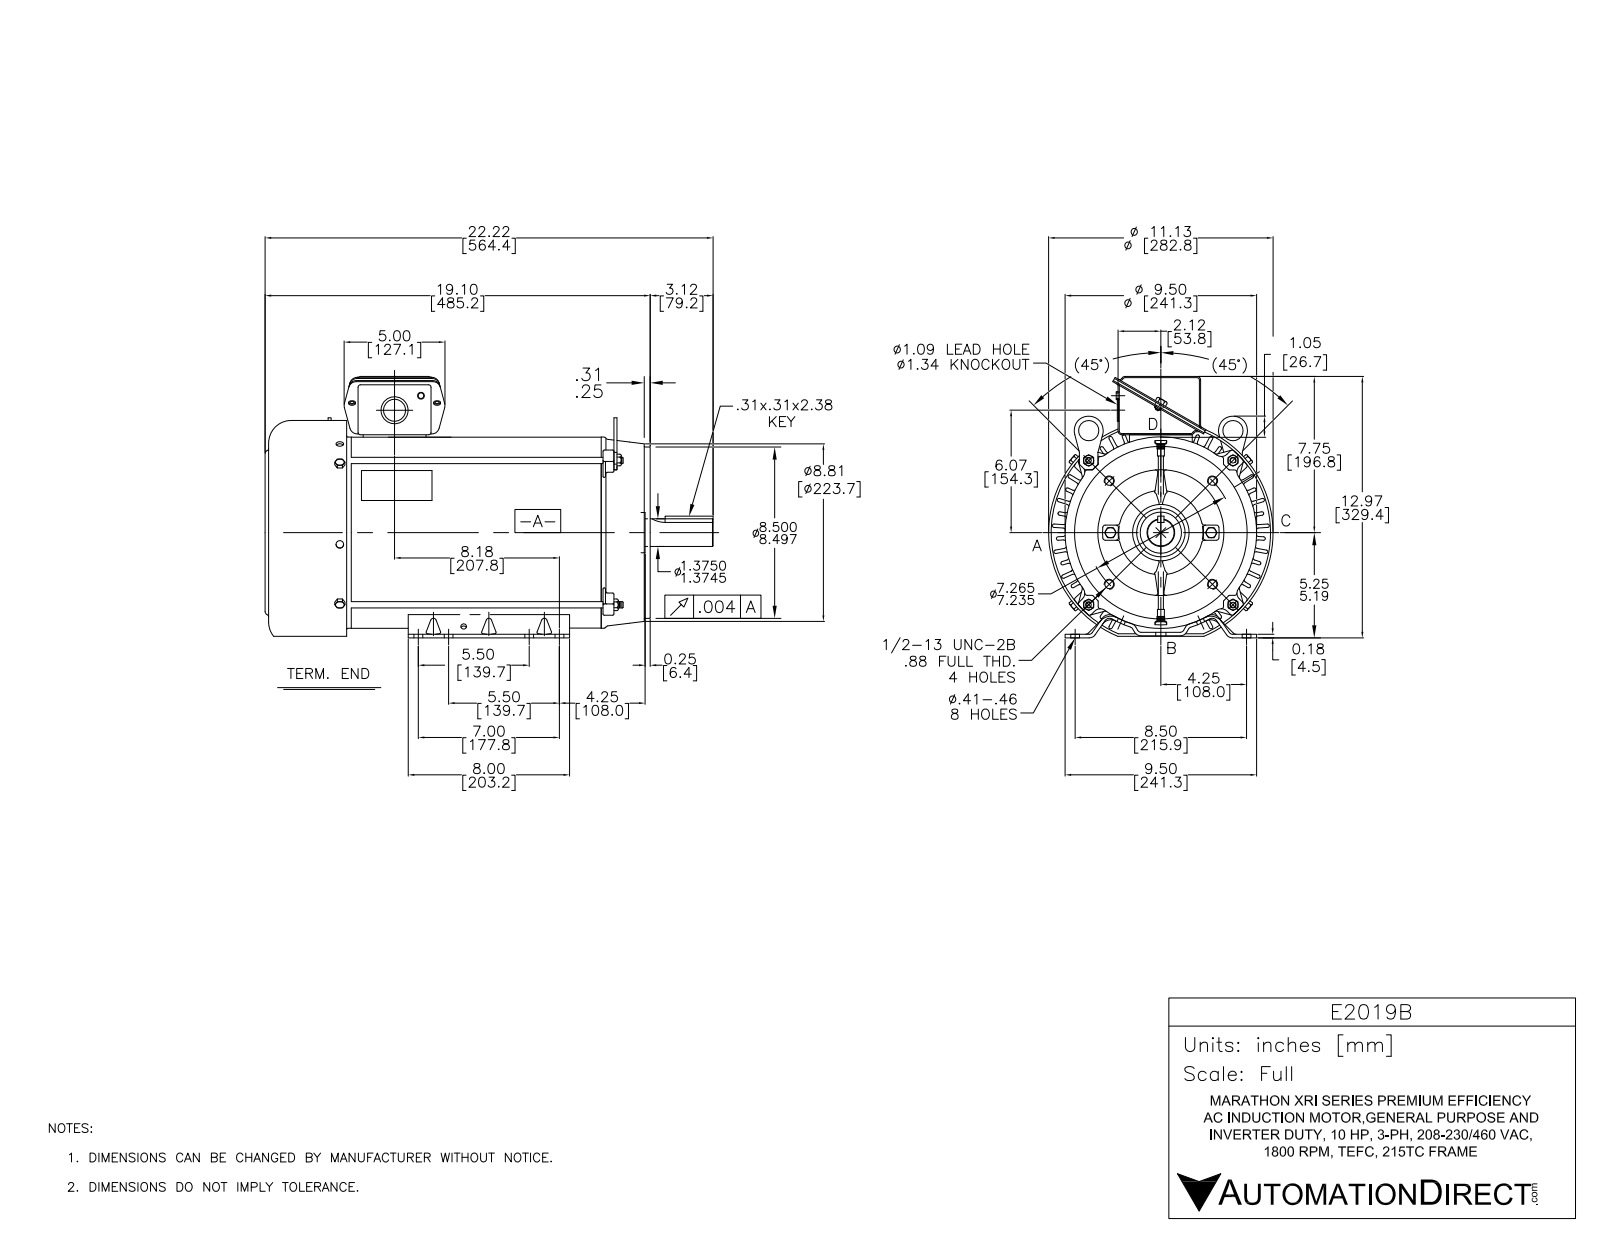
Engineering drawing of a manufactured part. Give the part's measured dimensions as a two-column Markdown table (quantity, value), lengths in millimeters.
| quantity | value |
| --- | --- |
| part name | E2019B r1 |
| STEP written by | SolidWorks 2017 (AUTOMOTIVE_DESIGN) |
| units | millimeters |
| bodies | 30 solids, 3332 faces (1052 planar, 1045 cylindrical, 1235 other) |
| overall size | 564.3 × 328 × 283.5 |
| volume | 3 118 000 mm³ |
| surface area | 1 408 000 mm² |
| round holes (diameter × count) | 9.5 × 10, 11 × 8, 6.5 × 4, 8.1 × 4, 9.4 × 4, 10.7 × 4, 5.6 × 3, 6.8 × 3, 4.5 × 2, 5.5 × 2, 7.1 × 2, 8.6 × 2 |
| round bosses / shafts (diameter × count) | 7.9 × 10, 11.2 × 6, 10.1 × 2, 7.5 × 2, 4.8 × 2, 241 × 1, 235.5 × 1, 215.9 × 1 |
| partial cylindrical surfaces (radius × count) | 3.3 × 149, 1.5 × 134, 3 × 86, 6.4 × 34, 0.8 × 12, 4.6 × 10, 1 × 8, 3.6 × 8 |
| main face-to-face distances | 1.5, 4.3, 480.7, 3, 4.5, 2.5, 69.4, 485, 4.5, 2.8 |
| hole center spacings | 158.1, 63.5, 108, 181.8, 25.4, 36.4, 38.1, 65.1 |
